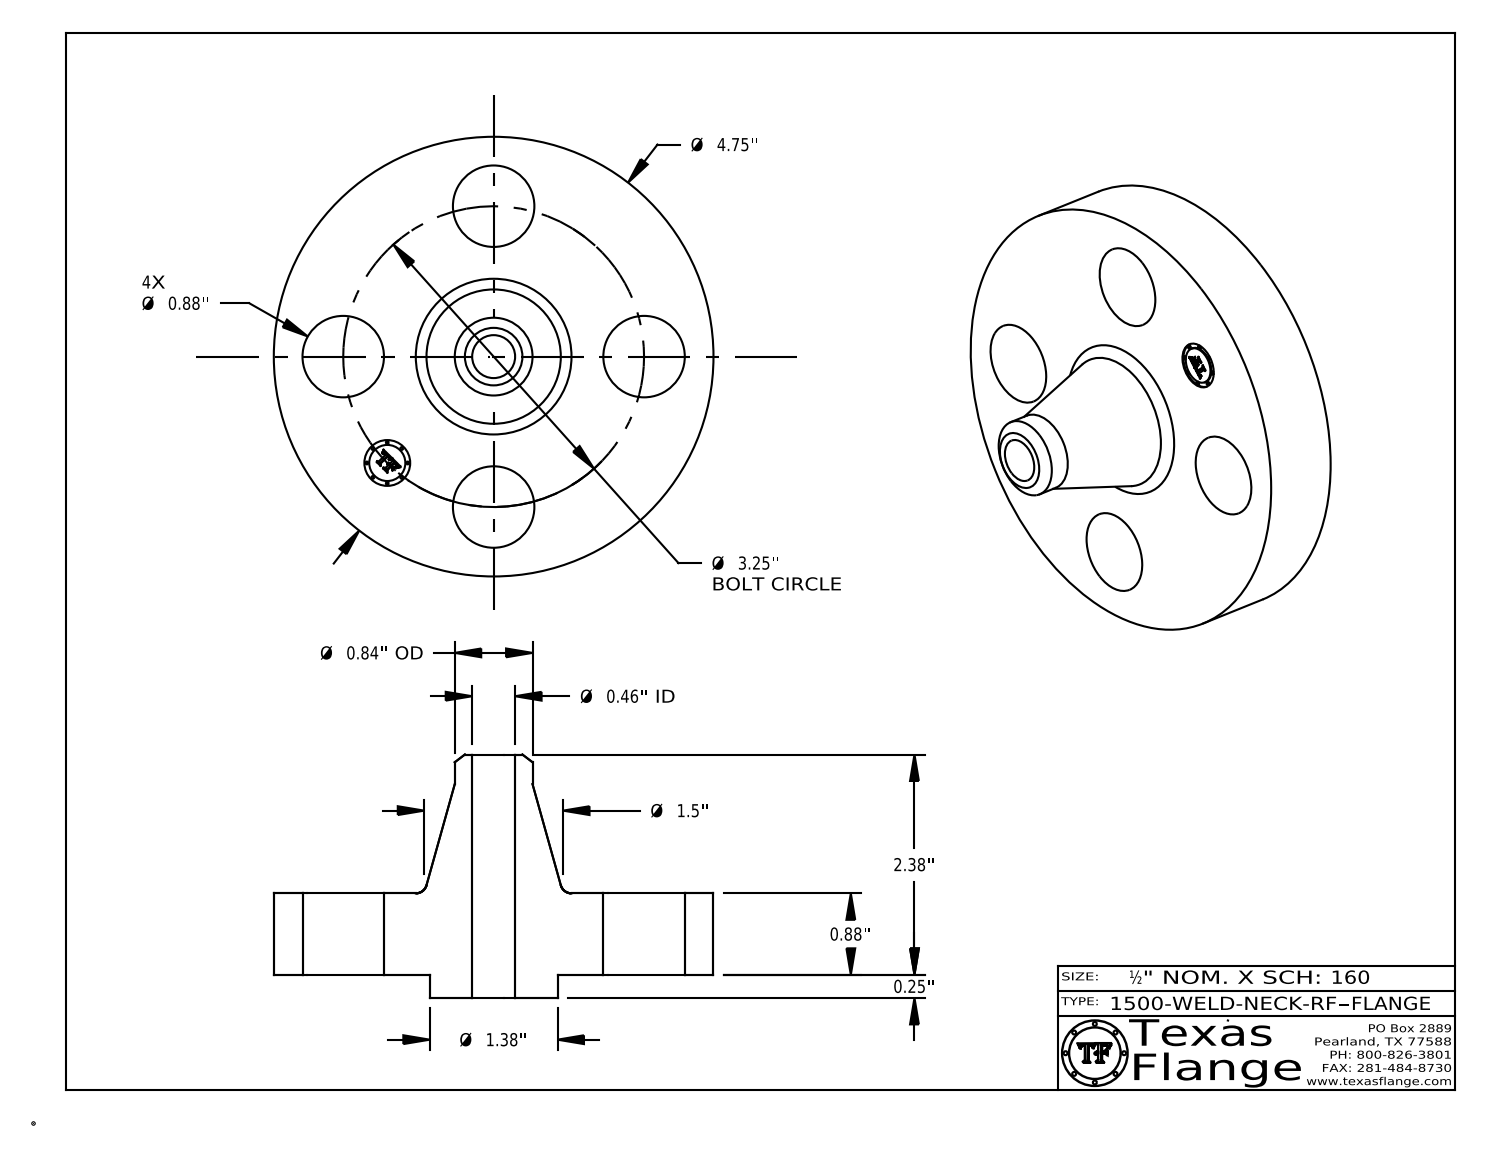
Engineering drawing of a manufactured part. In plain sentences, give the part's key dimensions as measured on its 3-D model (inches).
The part is named "1500-WELD-NECK-RF". Its 3-D file was written by "CATIA V5 STEP AP214 (AUTOMOTIVE_DESIGN)". It is 1 solid with 411 faces: 369 planar, 36 cylindrical and 6 other. Overall it measures 4.75 by 4.75 by 2.63 inches. Its volume is 14.86 cubic inches and its surface area 61.97 square inches. Round holes: 4 of diameter 0.88, 1 of diameter 0.464, 1 of diameter 0.495. Round bosses or shafts: 8 of diameter 0.03, 1 of diameter 4.75, 1 of diameter 1.38, 1 of diameter 0.84, 1 of diameter 0.39. The main face-to-face distances are 0.88, 0.25, 1.13, 2.63, 2.38, 1.5, 1.115, 0.865, 0.015, 1.515. The hole center spacings are 1.625, 2.298, 1.244, 3.003, 3.25.
